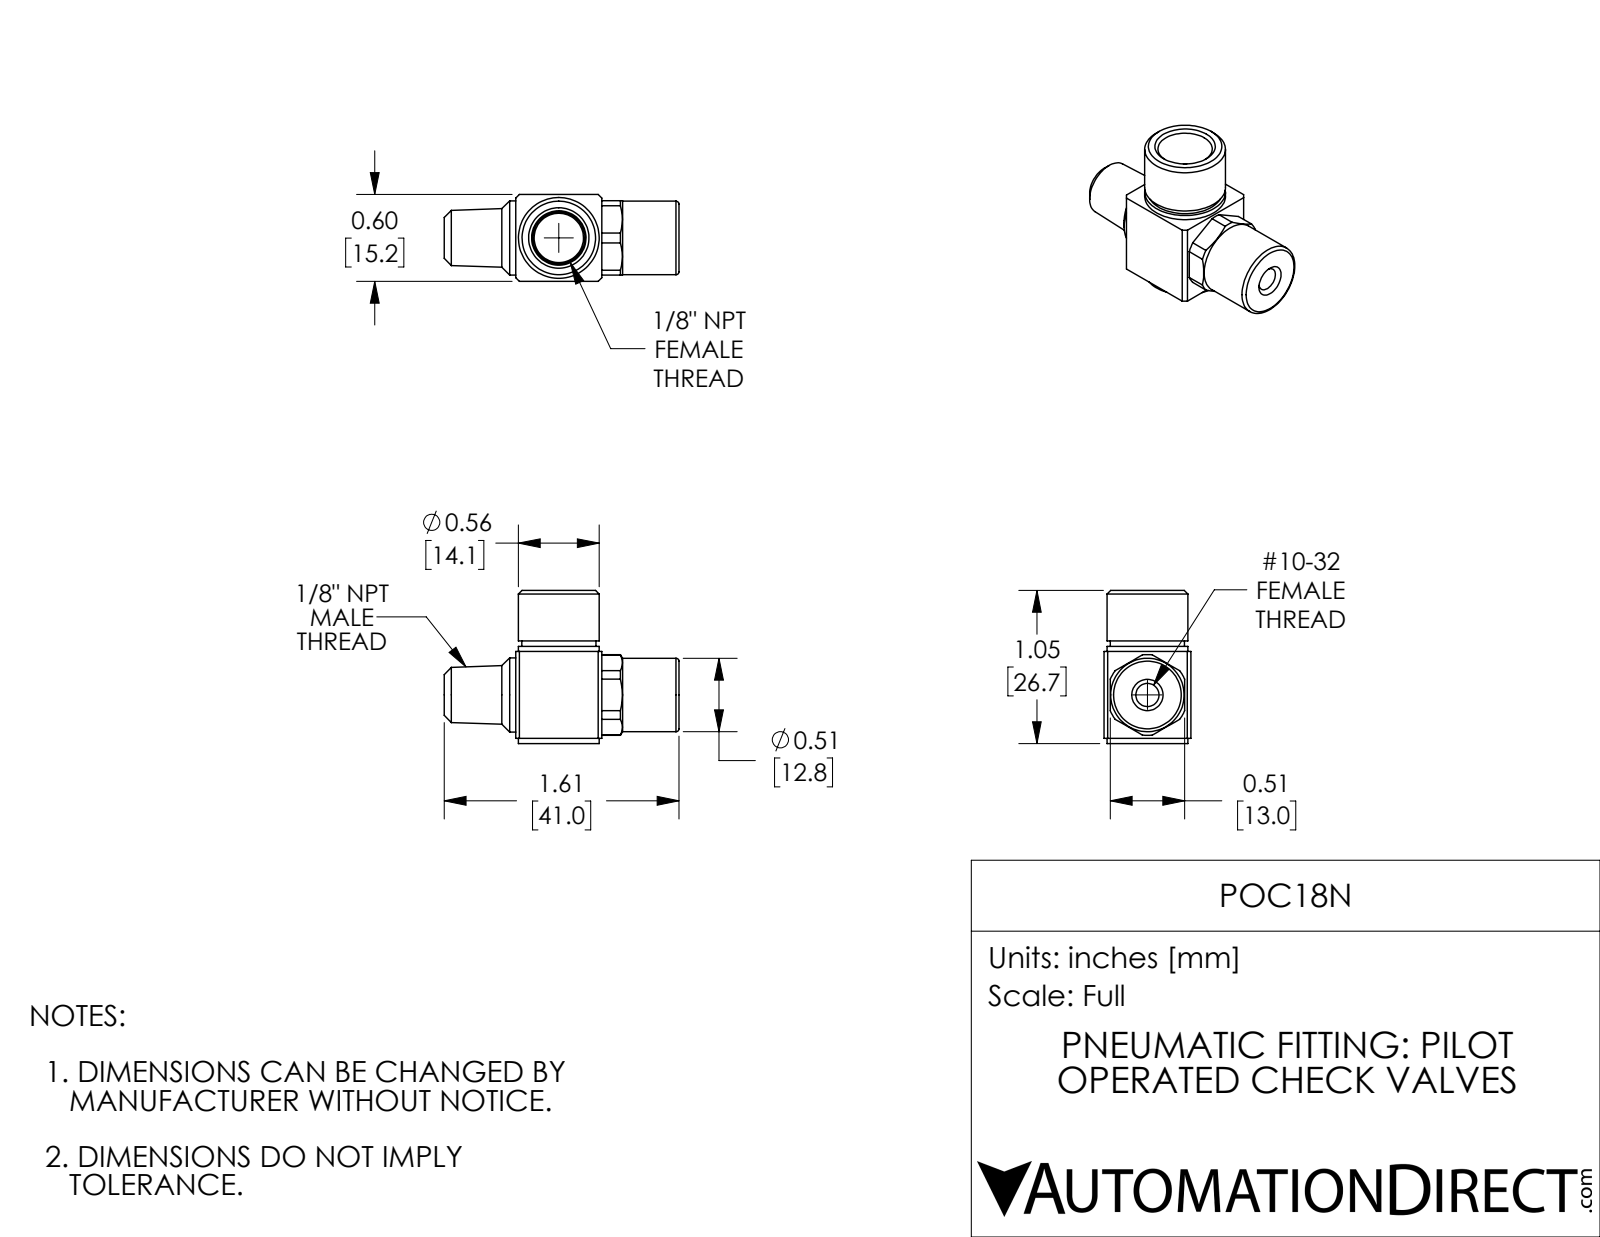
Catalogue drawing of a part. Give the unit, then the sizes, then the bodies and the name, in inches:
Units: inches
Overall size (bounding box): 1.614 × 1.052 × 0.597
Round holes (diameter × count): ⌀0.159 ×1, ⌀0.339 ×1
Round bosses / shafts (diameter × count): ⌀0.555 ×1, ⌀0.51 ×1, ⌀0.51 ×1, ⌀0.505 ×1
Partial cylindrical surfaces — rounded edges, fillets, slot ends (radius × count): R0.278 ×1
Main face-to-face distances: 0.597, 0.632, 0.035, 1.122, 0.592, 0.53, 0.511, 1.052, 1.017, 0.42
Volume: 0.381 in³ · Surface area: 5.773 in²
Bodies: 1 solid, 69 faces (23 planar, 24 cylindrical, 22 other)
Part name (STEP PRODUCT): POC18N
STEP written by: SolidWorks 2018 (AUTOMOTIVE_DESIGN)
